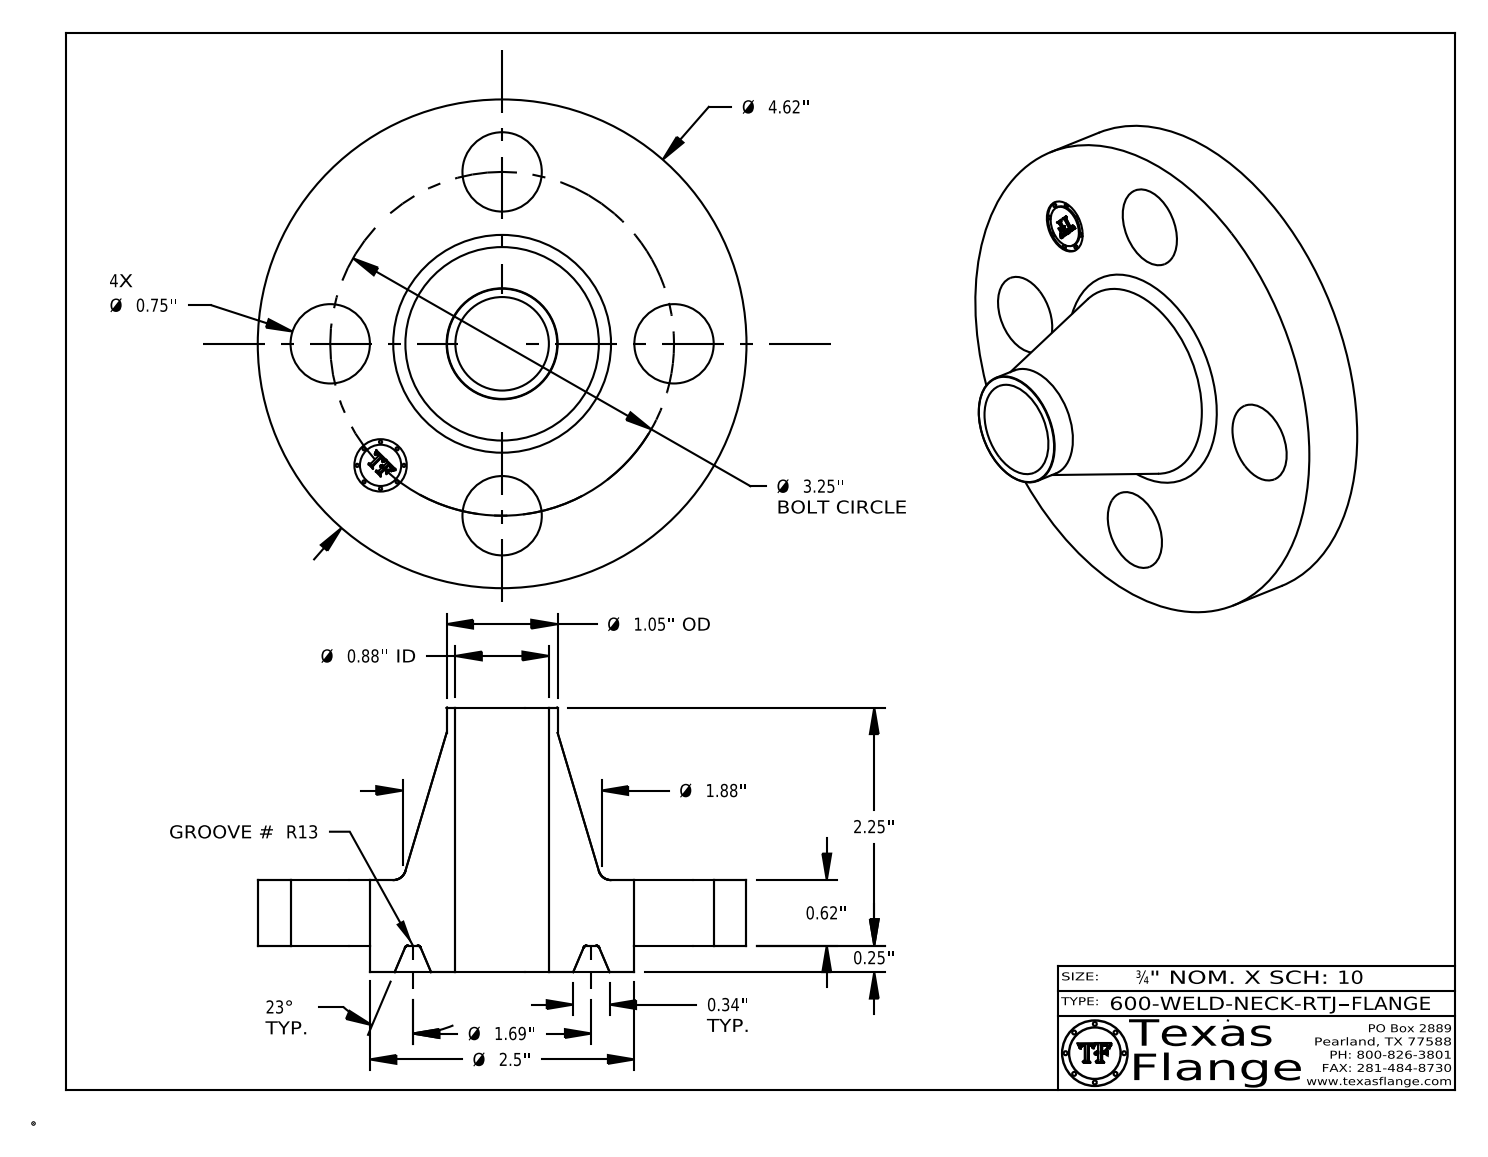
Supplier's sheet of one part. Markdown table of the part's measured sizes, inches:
| quantity | value |
| --- | --- |
| part name | 600-WELD-NECK-RTJ |
| STEP written by | CATIA V5 STEP AP214 (AUTOMOTIVE_DESIGN) |
| units | inches |
| bodies | 1 solid, 421 faces (371 planar, 36 cylindrical, 14 other) |
| overall size | 4.62 × 4.62 × 2.5 |
| volume | 11.3 in³ |
| surface area | 59.72 in² |
| round holes (diameter × count) | 0.75 × 4, 0.495 × 1, 0.884 × 1 |
| round bosses / shafts (diameter × count) | 0.03 × 8, 4.62 × 1, 2.5 × 1, 1.05 × 1, 0.39 × 1 |
| main face-to-face distances | 0.62, 0.25, 0.87, 2.5, 2.25, 1.63, 0.855, 0.605, 0.015, 1.645 |
| hole center spacings | 1.625, 2.298, 1.244, 3.003, 3.25 |
